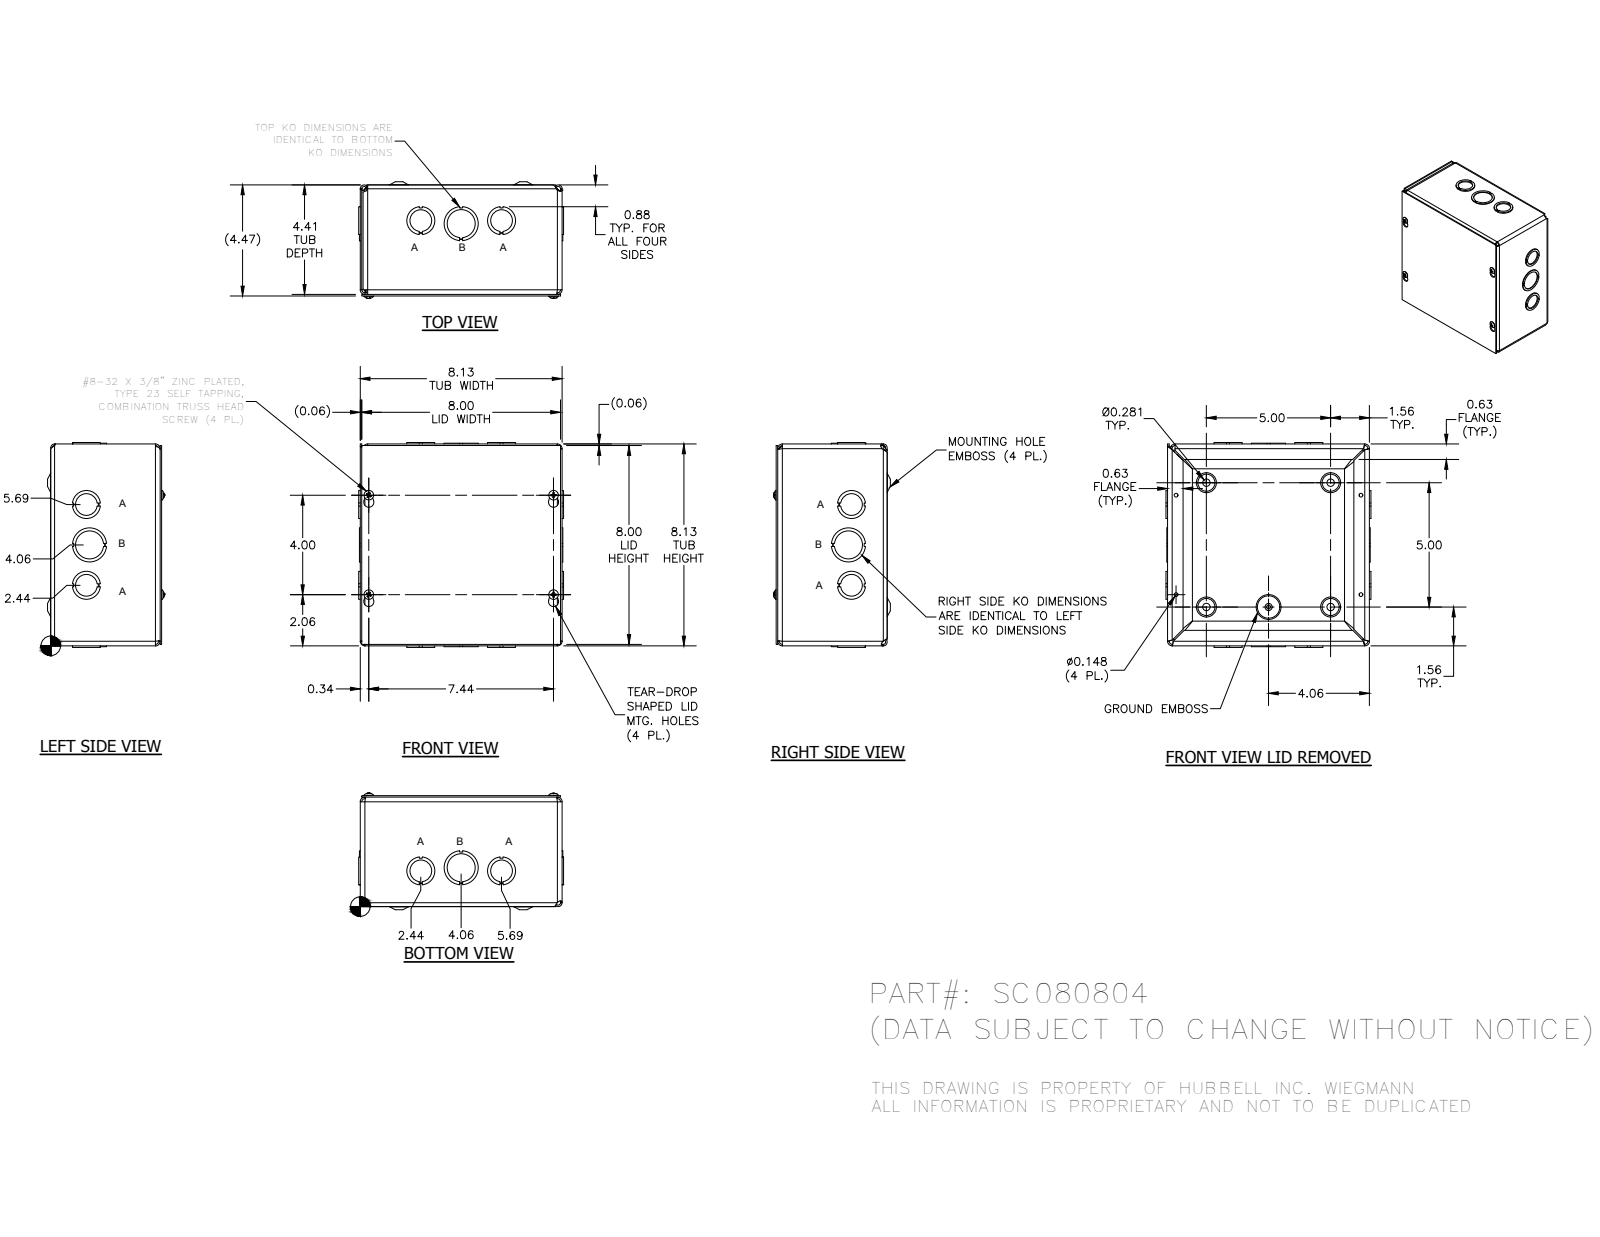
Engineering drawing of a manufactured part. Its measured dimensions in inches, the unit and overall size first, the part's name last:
Units: inches
Overall size (bounding box): 8.249 × 8.249 × 4.693
Round holes (diameter × count): ⌀1.125 ×6, ⌀0.148 ×4, ⌀0.3 ×4, ⌀0.875 ×4, ⌀1.375 ×2, ⌀0.165 ×1
Round bosses / shafts (diameter × count): ⌀0.384 ×4, ⌀0.164 ×4, ⌀0.228 ×1
Partial cylindrical surfaces — rounded edges, fillets, slot ends (radius × count): R0.125 ×12, R0.187 ×8, R0.055 ×4, R0.062 ×4, R0.094 ×4, R0.117 ×4, R0.124 ×4, R0.156 ×4
Main face-to-face distances: 0.062, 8.063, 4.343, 4.405, 8.001, 0.063, 4.406, 4.468, 0.062, 8.125
Hole centre spacings: 4.662, 5, 1.317, 1.317, 1.63, 1.63, 2.5, 3.25
Bodies: 22 solids, 694 faces (397 planar, 139 cylindrical, 158 other)
Part name (STEP PRODUCT): SC0808BKP; SC080804WRA; SC0808LID; 34056 (+1 more)
STEP written by: Autodesk Inventor 2014 (AUTOMOTIVE_DESIGN)
